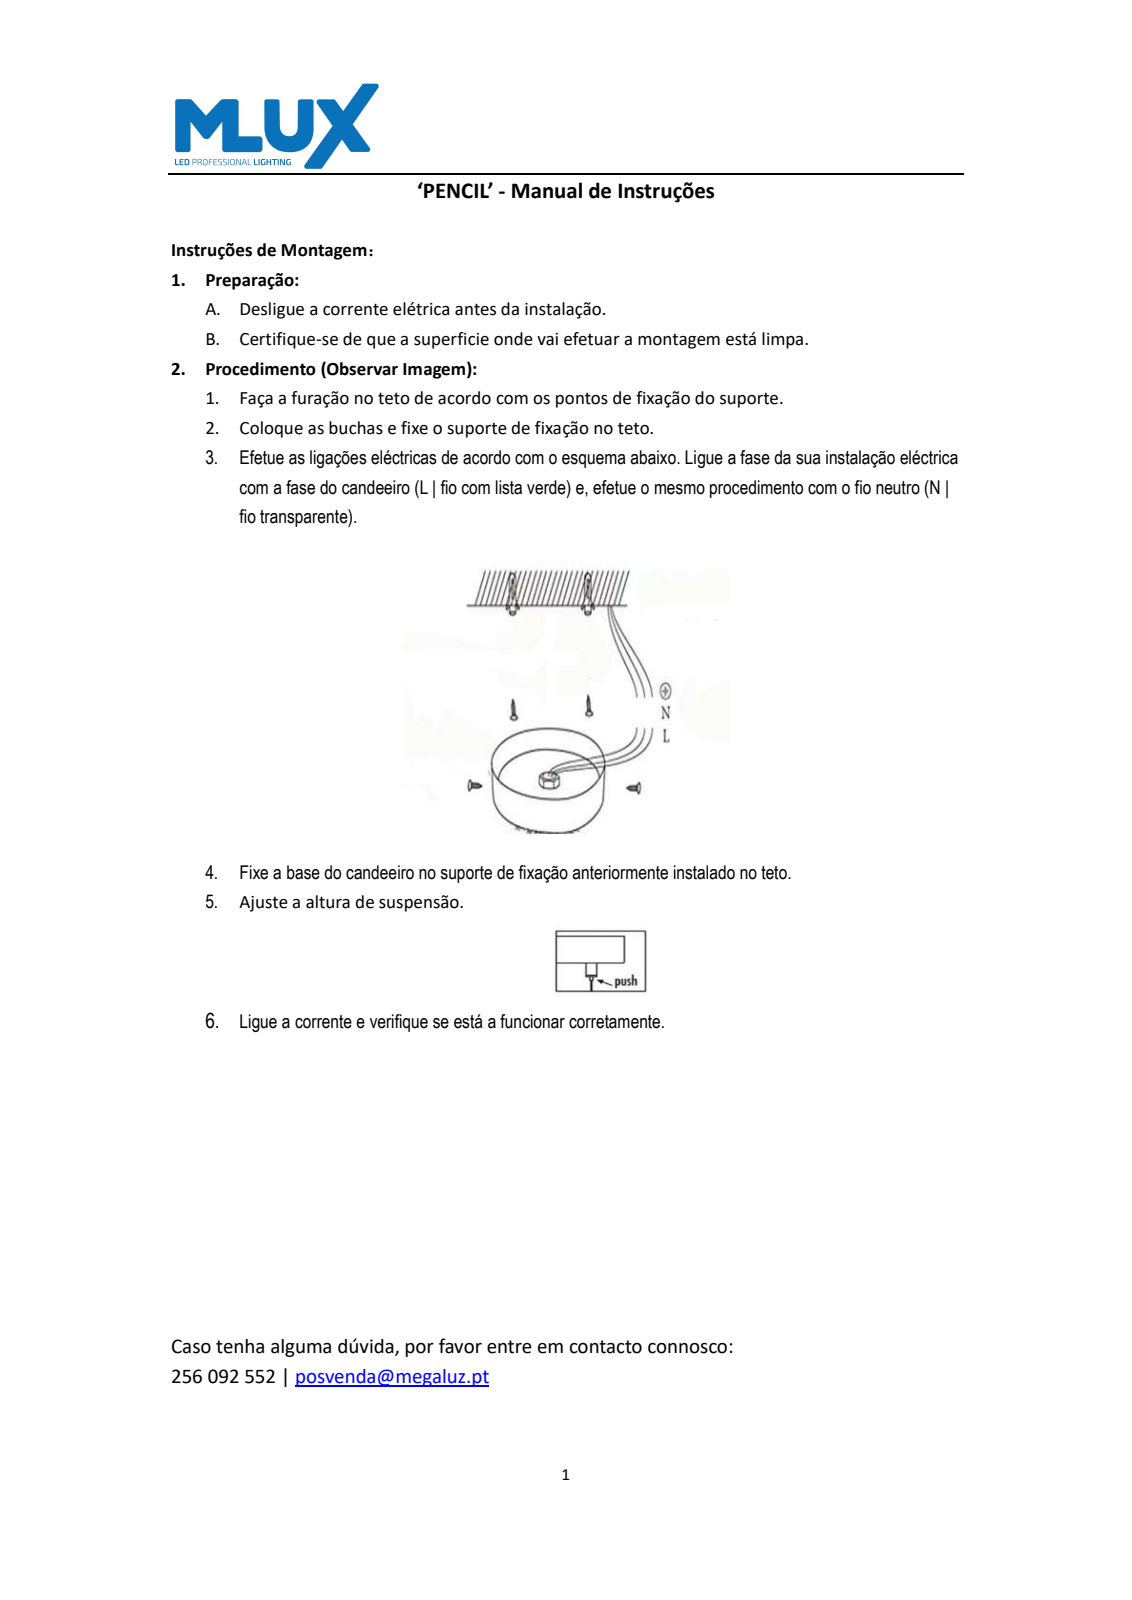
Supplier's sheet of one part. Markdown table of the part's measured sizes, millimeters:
| quantity | value |
| --- | --- |
| part name | DD-001-01-1; DD-001-01-2; DD-001-02; DD-001-03 (+6 more) |
| STEP written by | CREO PARAMETRIC BY PTC INC, 2020053 (CONFIG_CONTROL_DESIGN) |
| units | millimeters |
| bodies | 11 solids, 276 faces (82 planar, 124 cylindrical, 70 other) |
| overall size | 1435 × 63.92 × 60 |
| volume | 71 751 mm³ |
| surface area | 132 623 mm² |
| round holes (diameter × count) | 3.5 × 3, 2.5 × 1, 4.7 × 1, 5 × 1, 8 × 1, 30 × 1, 32 × 1, 38 × 1, 58 × 1 |
| round bosses / shafts (diameter × count) | 60 × 1, 40 × 1, 15 × 1, 8 × 1, 4.5 × 1, 4 × 1, 1.5 × 1 |
| partial cylindrical surfaces (radius × count) | 0.3 × 8, 1.75 × 4, 1 × 2, 2 × 2, 2.25 × 2, 3 × 2 |
| main face-to-face distances | 1, 1001, 1035, 34, 1000, 385, 1385, 1386, 384, 1002 |
| hole center spacings | 8, 16 |
